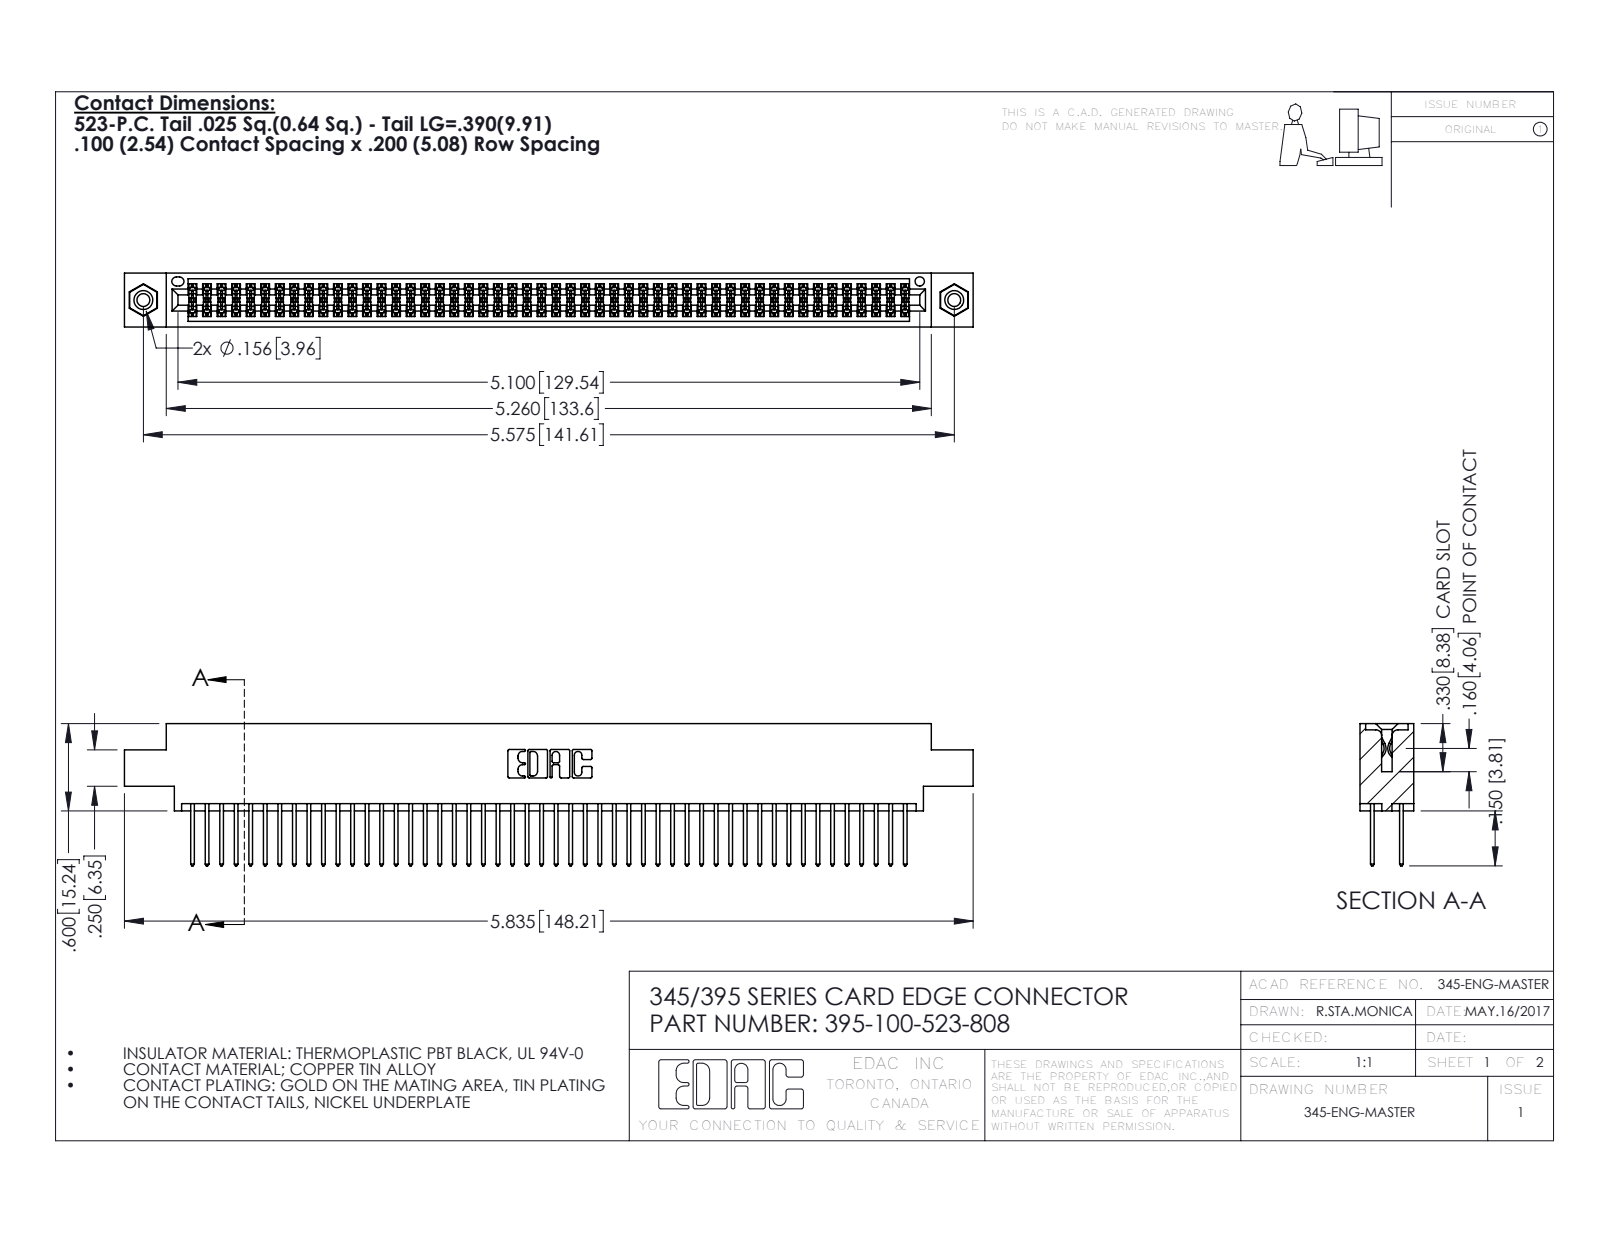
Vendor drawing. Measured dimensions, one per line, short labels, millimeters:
name: 345 Part_0.170 Offset - 0.156 Dia-TI; 395-100-523-808; 345-292-001_345-293-123; 345-250-001_345-250-003-102
written by: SolidWorks 2016 (CONFIG_CONTROL_DESIGN)
unit: mm
bodies: 103 solids, 5190 faces (3416 planar, 1758 cylindrical, 16 other)
size: 148.2 × 24.8 × 9.4
volume: 14 600 mm³; area: 22 750 mm²
holes: 2× ⌀2.3, 2× ⌀3.2, 2× ⌀4, 1× ⌀1.6
bosses: 2× ⌀3.9
rounds: 150× R0.2, 100× R0.3, 22× R0.3, 6× R0.2, 6× R0.8, 3× R0.7, 2× R0.4, 2× R0.5
face distances: 1.8, 7.6, 5.1, 2.5, 6.9, 0.6, 9.4, 5.7, 4.4, 3.8
hole spacings: 6.9, 135.6, 141.6
